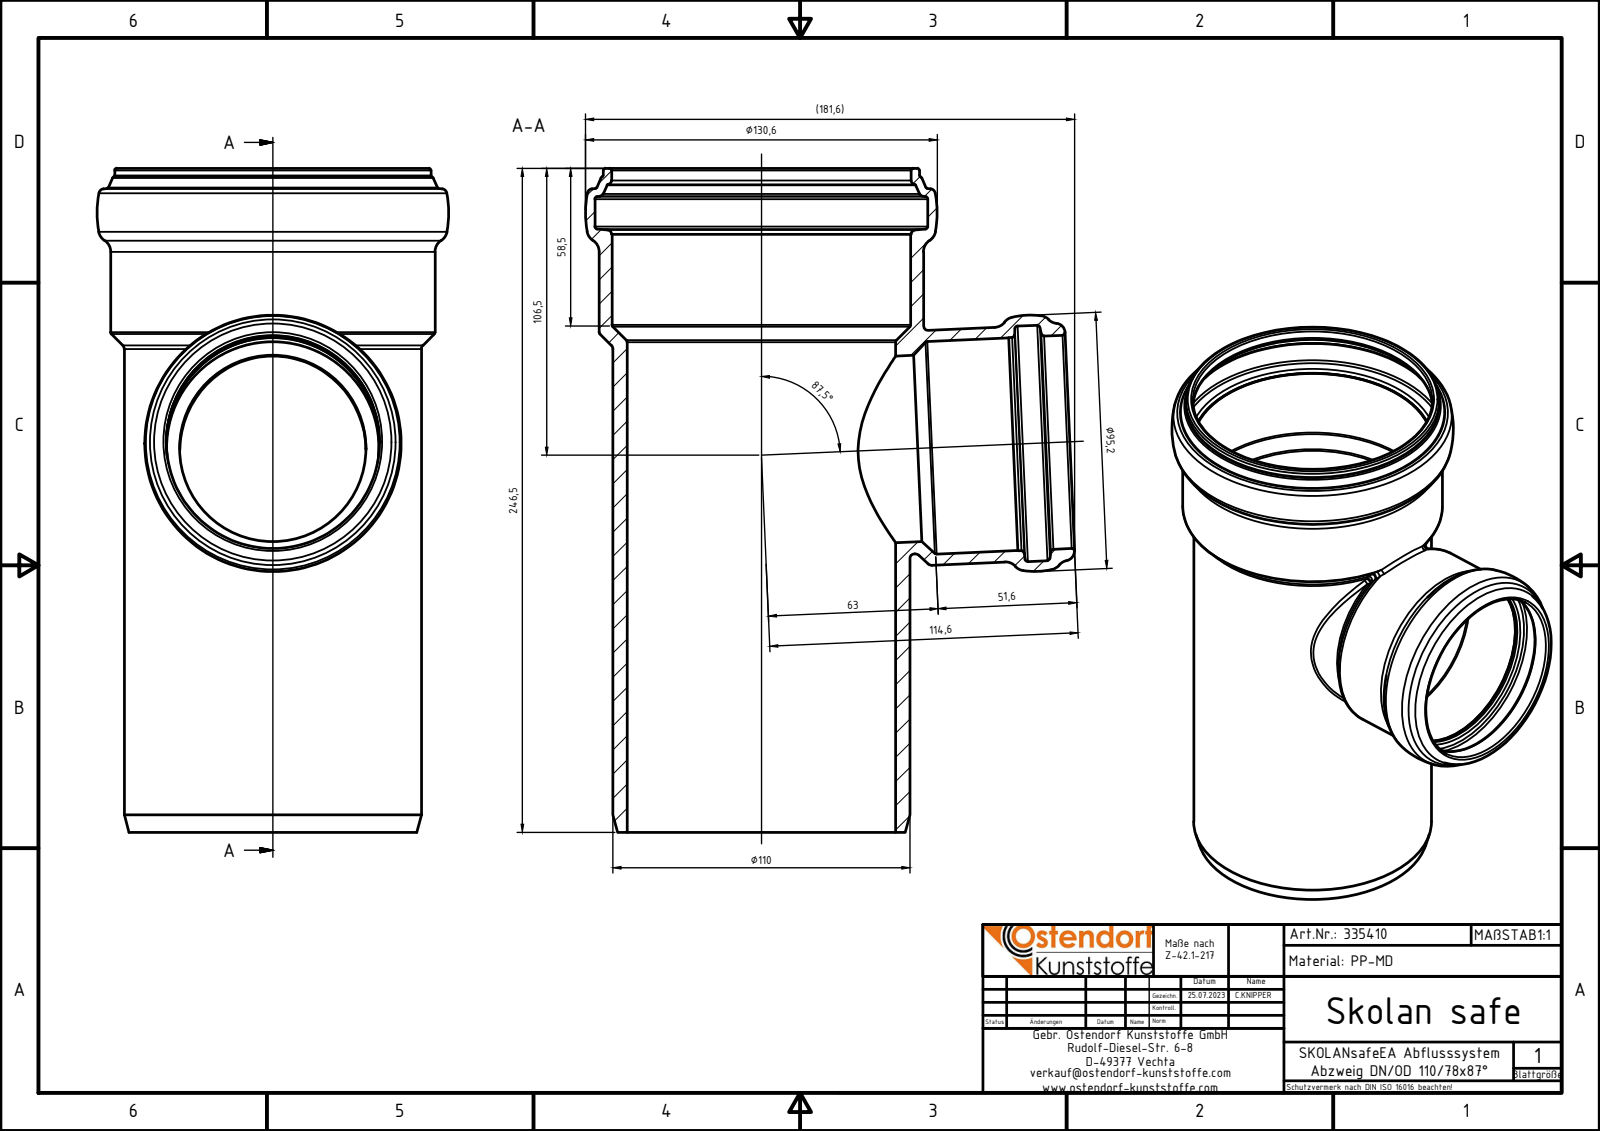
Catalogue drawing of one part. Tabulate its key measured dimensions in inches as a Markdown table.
| quantity | value |
| --- | --- |
| part name | 335410z |
| STEP written by | Autodesk Inventor 2020 (AUTOMOTIVE_DESIGN) |
| units | inches |
| bodies | 1 solid, 104 faces (7 planar, 15 cylindrical, 82 other) |
| overall size | 9.705 × 8.599 × 5.142 |
| volume | 31.85 in³ |
| surface area | 342.5 in² |
| round holes (diameter × count) | 3.118 × 2, 2.724 × 1, 3.11 × 1, 3.457 × 1, 3.925 × 1, 4.366 × 1, 4.378 × 1, 4.866 × 1 |
| round bosses / shafts (diameter × count) | 4.744 × 1, 4.622 × 1, 4.343 × 1, 3.433 × 1, 3.079 × 1 |
| main face-to-face distances | 9.705, 8.74, 0.965, 0.118 |
